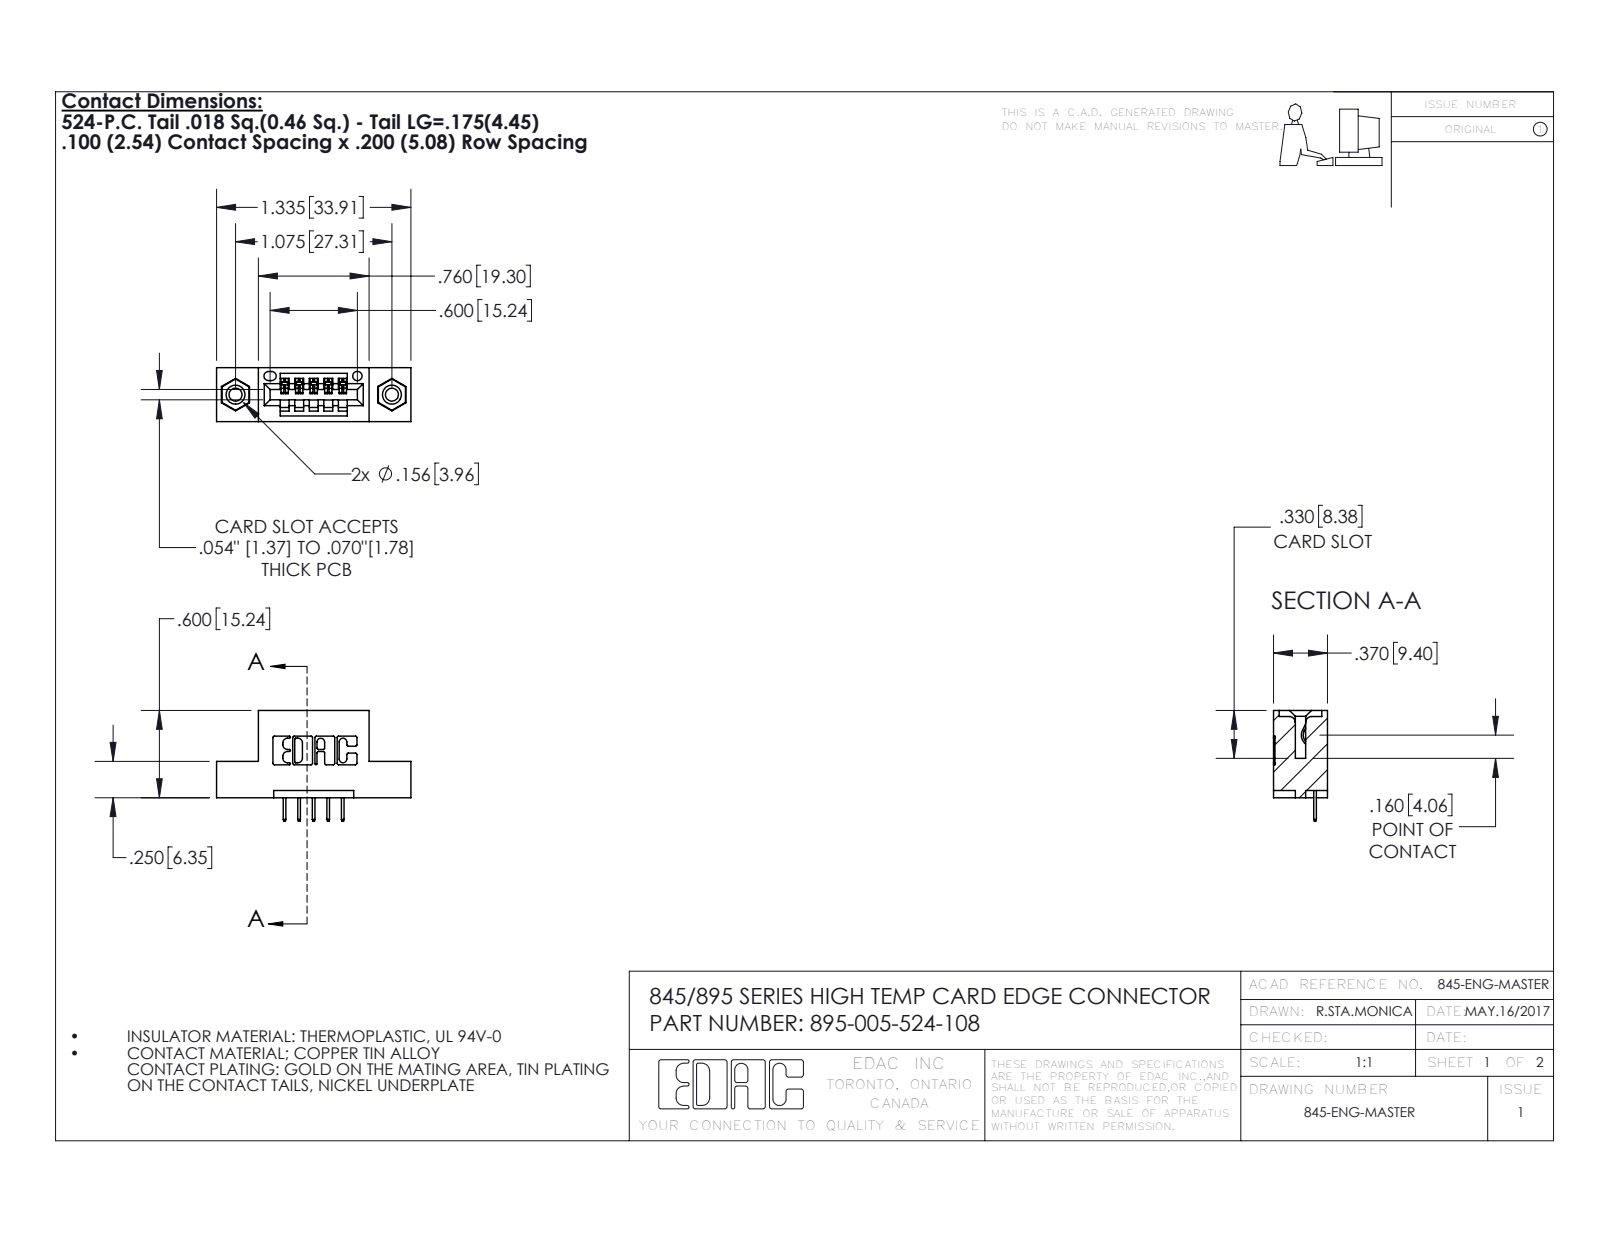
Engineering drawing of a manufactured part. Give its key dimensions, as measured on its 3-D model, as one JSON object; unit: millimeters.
{"part_name": "395-005-524-108; 345-292-001_345-293-124; 345-250-001_345-250-003-102; 345 Part_Flush Mounting Lugs - 0.156 Dia-TI", "step_written_by": "SolidWorks 2016 (CONFIG_CONTROL_DESIGN)", "units": "millimeters", "bodies": {"solids": 8, "faces": 496, "planar": 342, "cylindrical": 138, "other": 16}, "overall_size": [33.9, 19.4, 9.4], "volume_mm3": 2880, "surface_area_mm2": 3295, "round_holes": [[2.3, 2], [3.2, 2], [4, 2], [1.6, 1]], "round_bosses_or_shafts": [[3.9, 2]], "partial_cylinders_radius": [[0.3, 22], [0.2, 10], [0.2, 6], [0.8, 6], [0.7, 3], [0.8, 2], [1, 2], [0.4, 1]], "face_to_face_distances": [5.1, 9.4, 2.5, 1.8, 7.6, 8.9, 6.4, 1.5, 14, 0.6], "hole_center_spacings": [6.9, 21.5, 27.3]}
